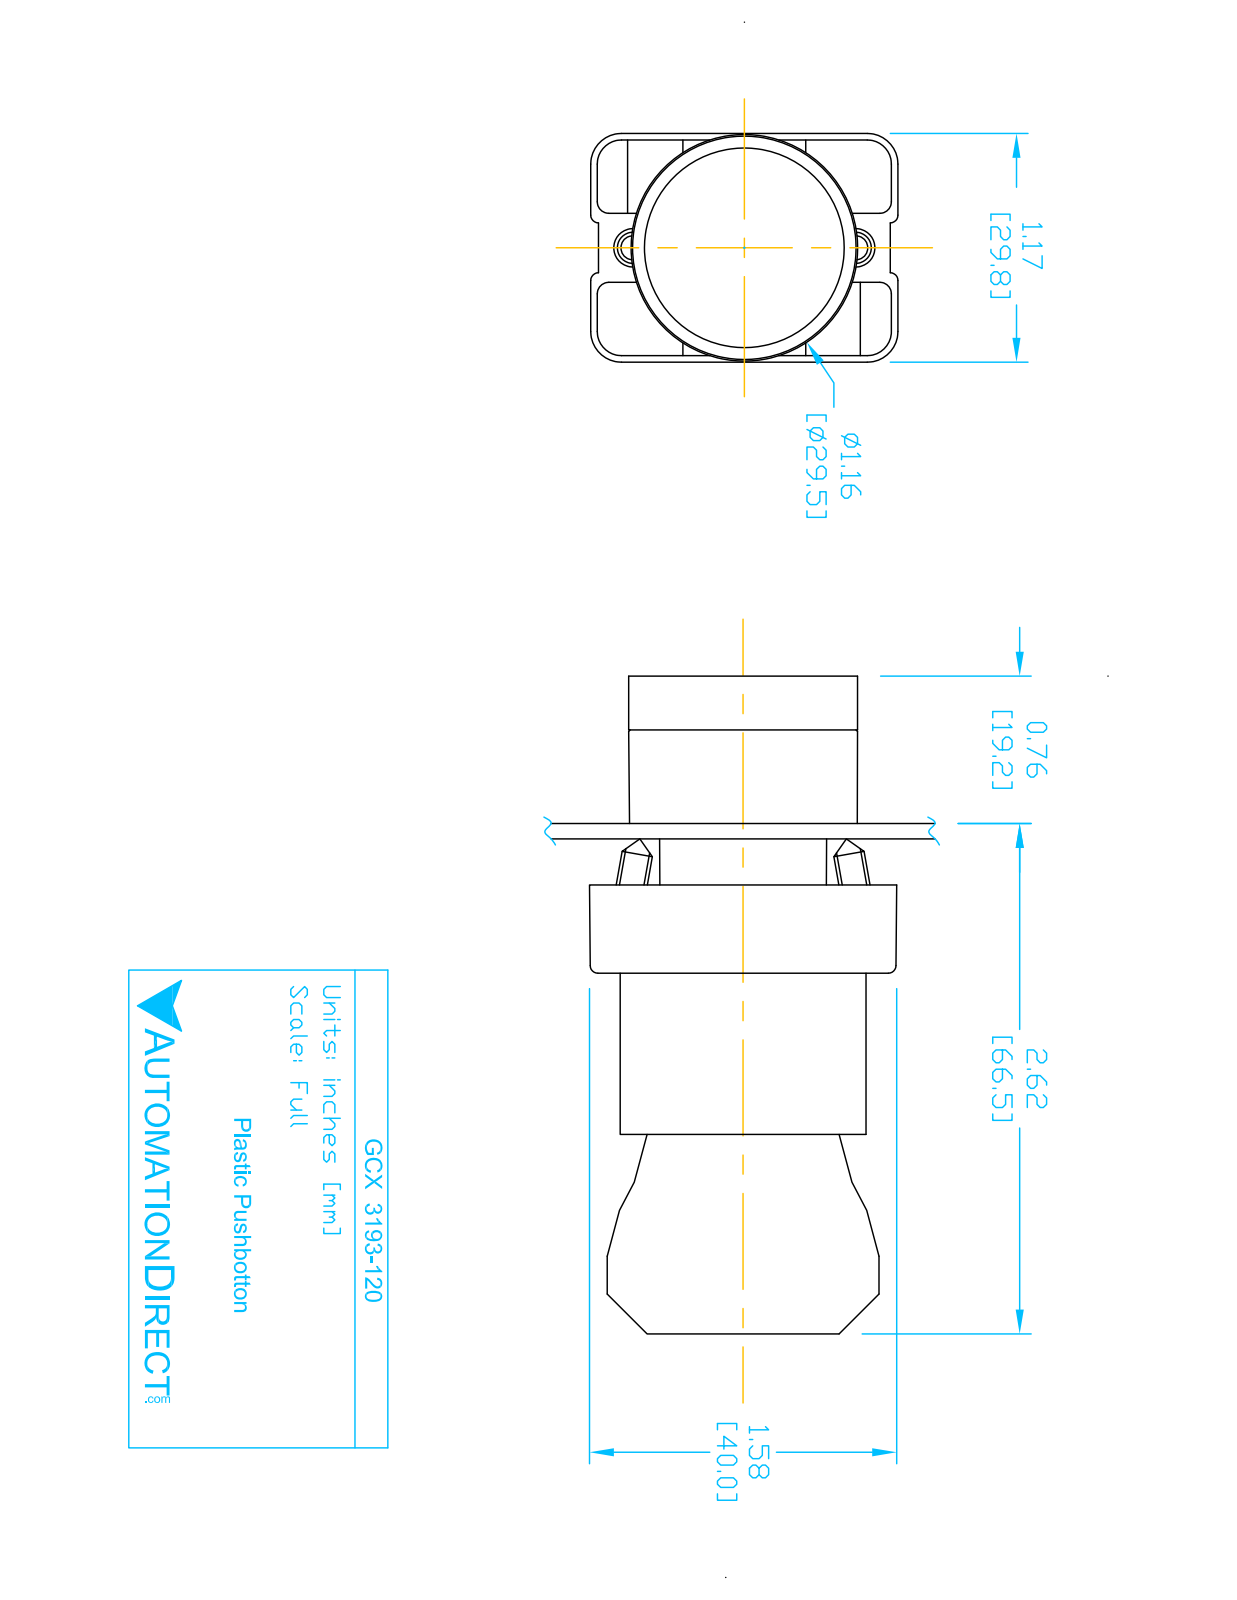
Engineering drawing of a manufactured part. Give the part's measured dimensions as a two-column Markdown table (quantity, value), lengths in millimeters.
| quantity | value |
| --- | --- |
| part name | GCX3193-120; ECX3029-2; ECX1050; GCX3193 OPERATOR (+1 more) |
| STEP written by | SolidWorks 2016 (AUTOMOTIVE_DESIGN) |
| units | millimeters |
| bodies | 8 solids, 431 faces (252 planar, 148 cylindrical, 31 other) |
| overall size | 84.3 × 40.2 × 29.9 |
| volume | 45 790 mm³ |
| surface area | 25 010 mm² |
| round holes (diameter × count) | 2 × 2, 3.1 × 2, 3.3 × 2, 2.2 × 1, 5 × 1, 11.9 × 1, 22.3 × 1, 22.6 × 1, 26 × 1 |
| round bosses / shafts (diameter × count) | 4 × 4, 29.8 × 1, 25.5 × 1, 24 × 1, 21.7 × 1, 19.8 × 1, 12.8 × 1 |
| partial cylindrical surfaces (radius × count) | 1.5 × 24, 1 × 12, 3.1 × 12, 4 × 12, 1 × 8, 3.3 × 2, 0.5 × 1, 1.6 × 1 |
| main face-to-face distances | 21, 14.7, 51.3, 30.3, 29.7, 7, 58.3, 37.3, 0.8, 0.8 |
| hole center spacings | 6, 13.8, 12, 12.4 |
